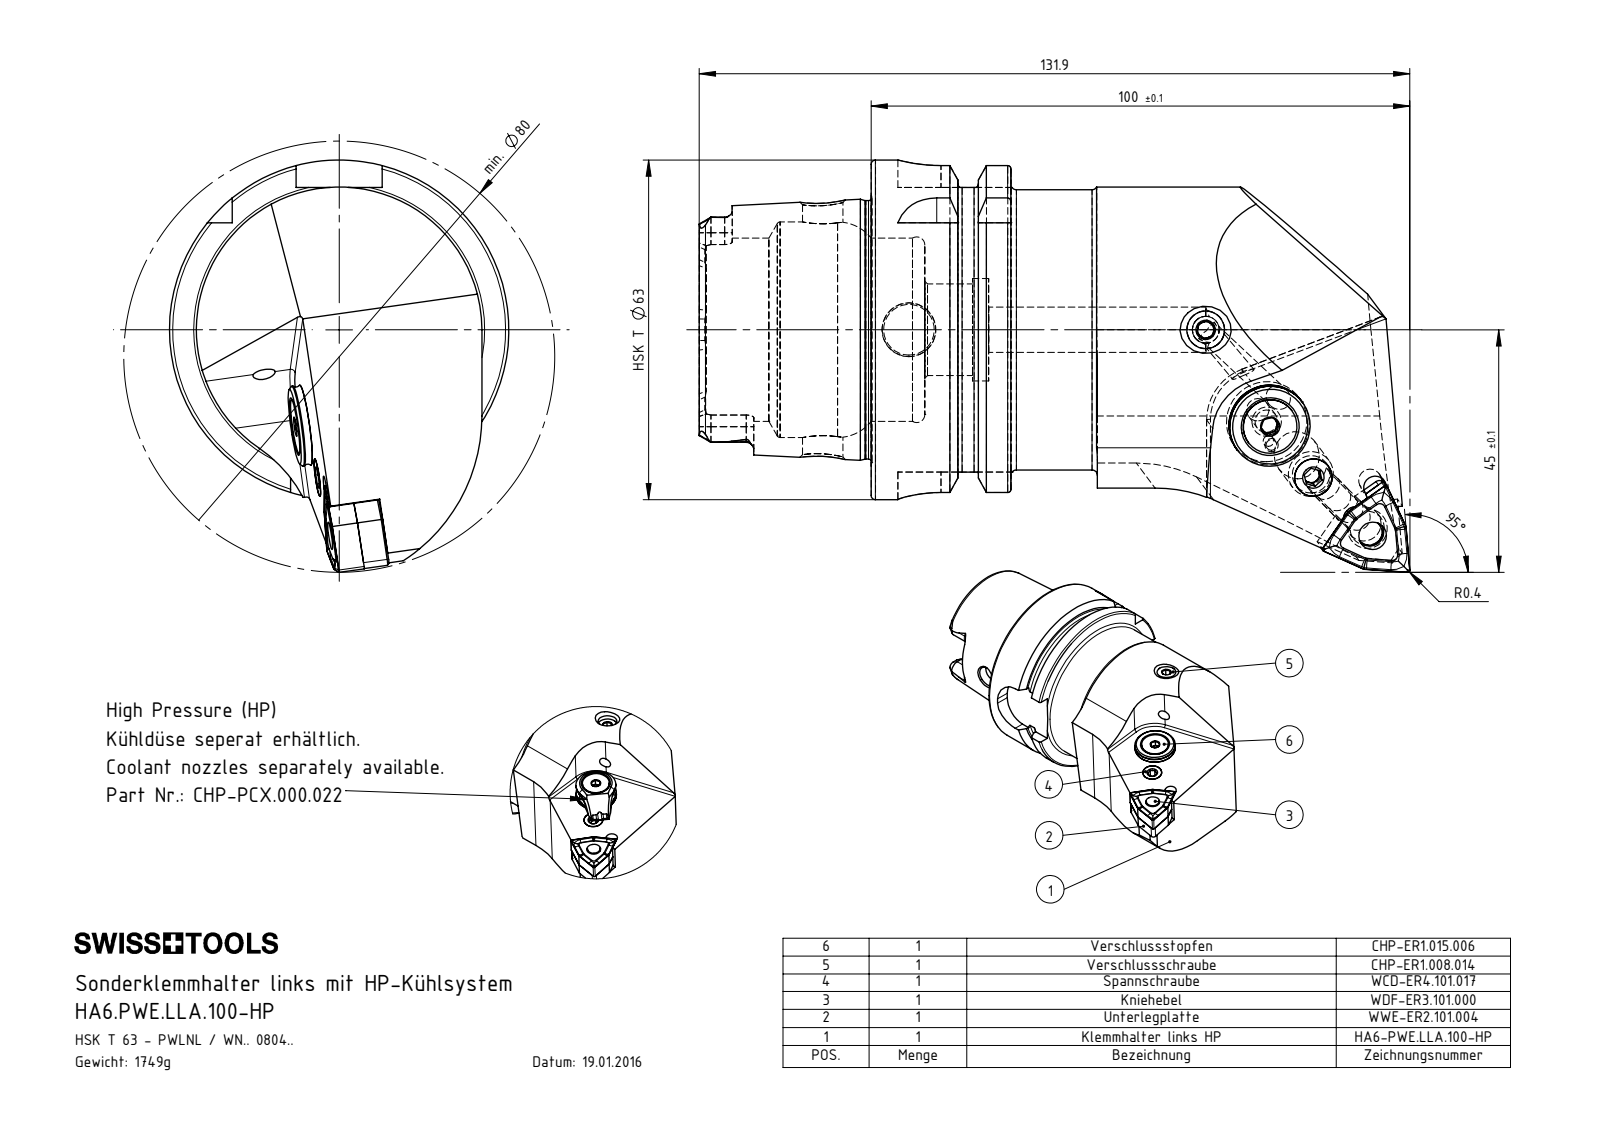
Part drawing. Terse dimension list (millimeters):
name: CHP-PCX.000.022_B; WCD-ER1.101.000; ISO 8752 2x8; HA6-PWE.LLA.100-HP (+8 more)
written by: SolidWorks 2015 (AUTOMOTIVE_DESIGN)
unit: mm
bodies: 15 solids, 690 faces (201 planar, 188 cylindrical, 301 other)
size: 131.9 × 76.5 × 63
volume: 224 331 mm³; area: 44 266 mm²
holes: 3× ⌀4.2, 2× ⌀7, 2× ⌀8.4, 1× ⌀1.2, 1× ⌀2, 1× ⌀2.5, 1× ⌀3, 1× ⌀5, 1× ⌀5.16, 1× ⌀5.2, 1× ⌀5.3, 1× ⌀6.7
bosses: 2× ⌀13.4, 2× ⌀10, 2× ⌀8, 2× ⌀5, 1× ⌀63, 1× ⌀54.95, 1× ⌀52, 1× ⌀47.94
rounds: 10× R1, 6× R1.4, 4× R2.88, 4× R8, 3× R0.4, 3× R2.5, 3× R6, 2× R0.5
face distances: 25.95, 16, 9.95, 31.9, 41.85, 57.85, 52.8, 21.8, 11.85, 9.22
hole spacings: 24.74, 28.5, 4.48, 4.5, 9.2, 4.49, 12.93, 12.94
